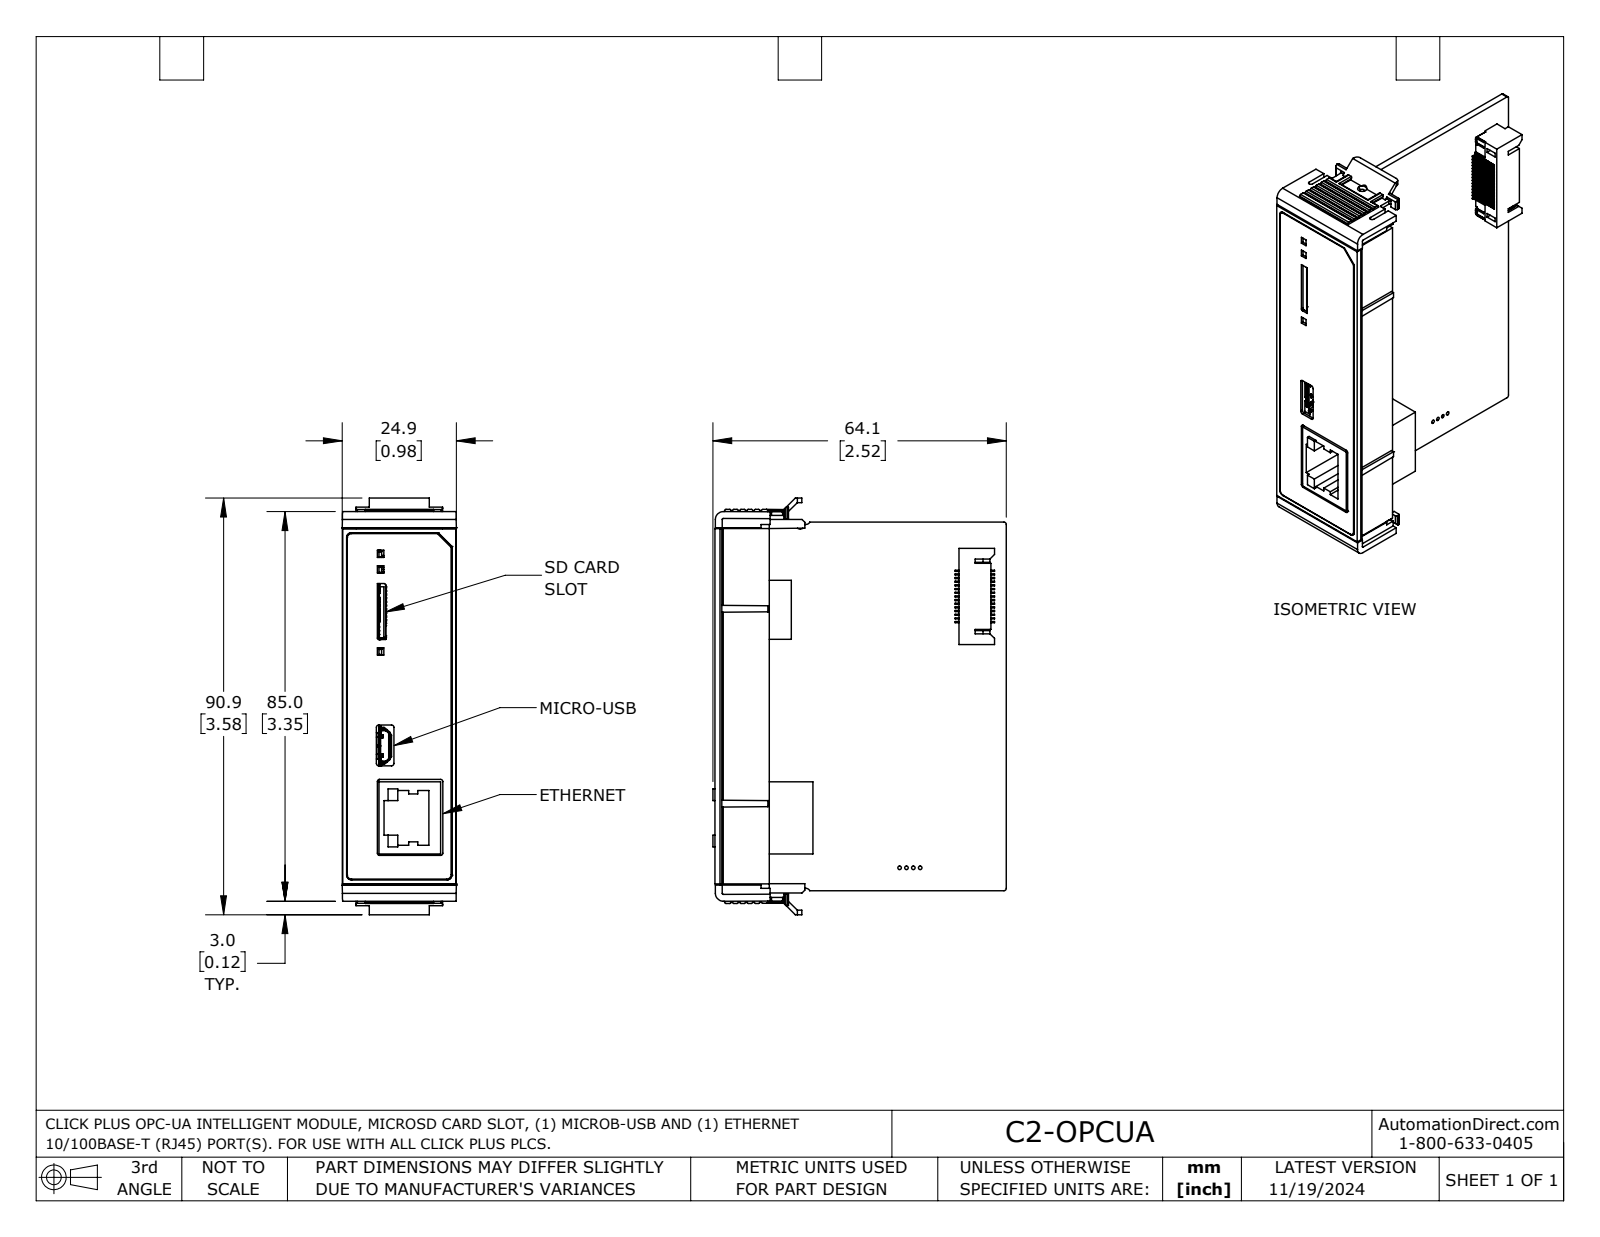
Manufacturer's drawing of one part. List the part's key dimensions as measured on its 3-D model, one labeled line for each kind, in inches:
Part name (STEP PRODUCT): C2-OPCUA_3D
STEP written by: SolidWorks 2024 (AUTOMOTIVE_DESIGN)
Units: inches
Bodies: 2 solids, 2131 faces (1788 planar, 310 cylindrical, 33 other)
Overall size (bounding box): 3.579 × 2.524 × 0.98
Volume: 1.138 in³ · Surface area: 41.55 in²
Round holes (diameter × count): ⌀0.031 ×4, ⌀0.016 ×2
Round bosses / shafts (diameter × count): ⌀0.031 ×12, ⌀0.128 ×2, ⌀0.059 ×2
Partial cylindrical surfaces — rounded edges, fillets, slot ends (radius × count): R0.012 ×81, R0.004 ×32, R0.02 ×22, R0.039 ×17, R0.024 ×15, R0.008 ×14, R0.006 ×12, R0.01 ×10
Main face-to-face distances: 0.063, 0.02, 0.851, 0.846, 0.073, 0.054, 0.067, 0.039, 0.593, 0.53
Hole centre spacings: 0.059, 0.118, 0.177, 0.287, 1.697, 1.748, 1.798, 1.85
